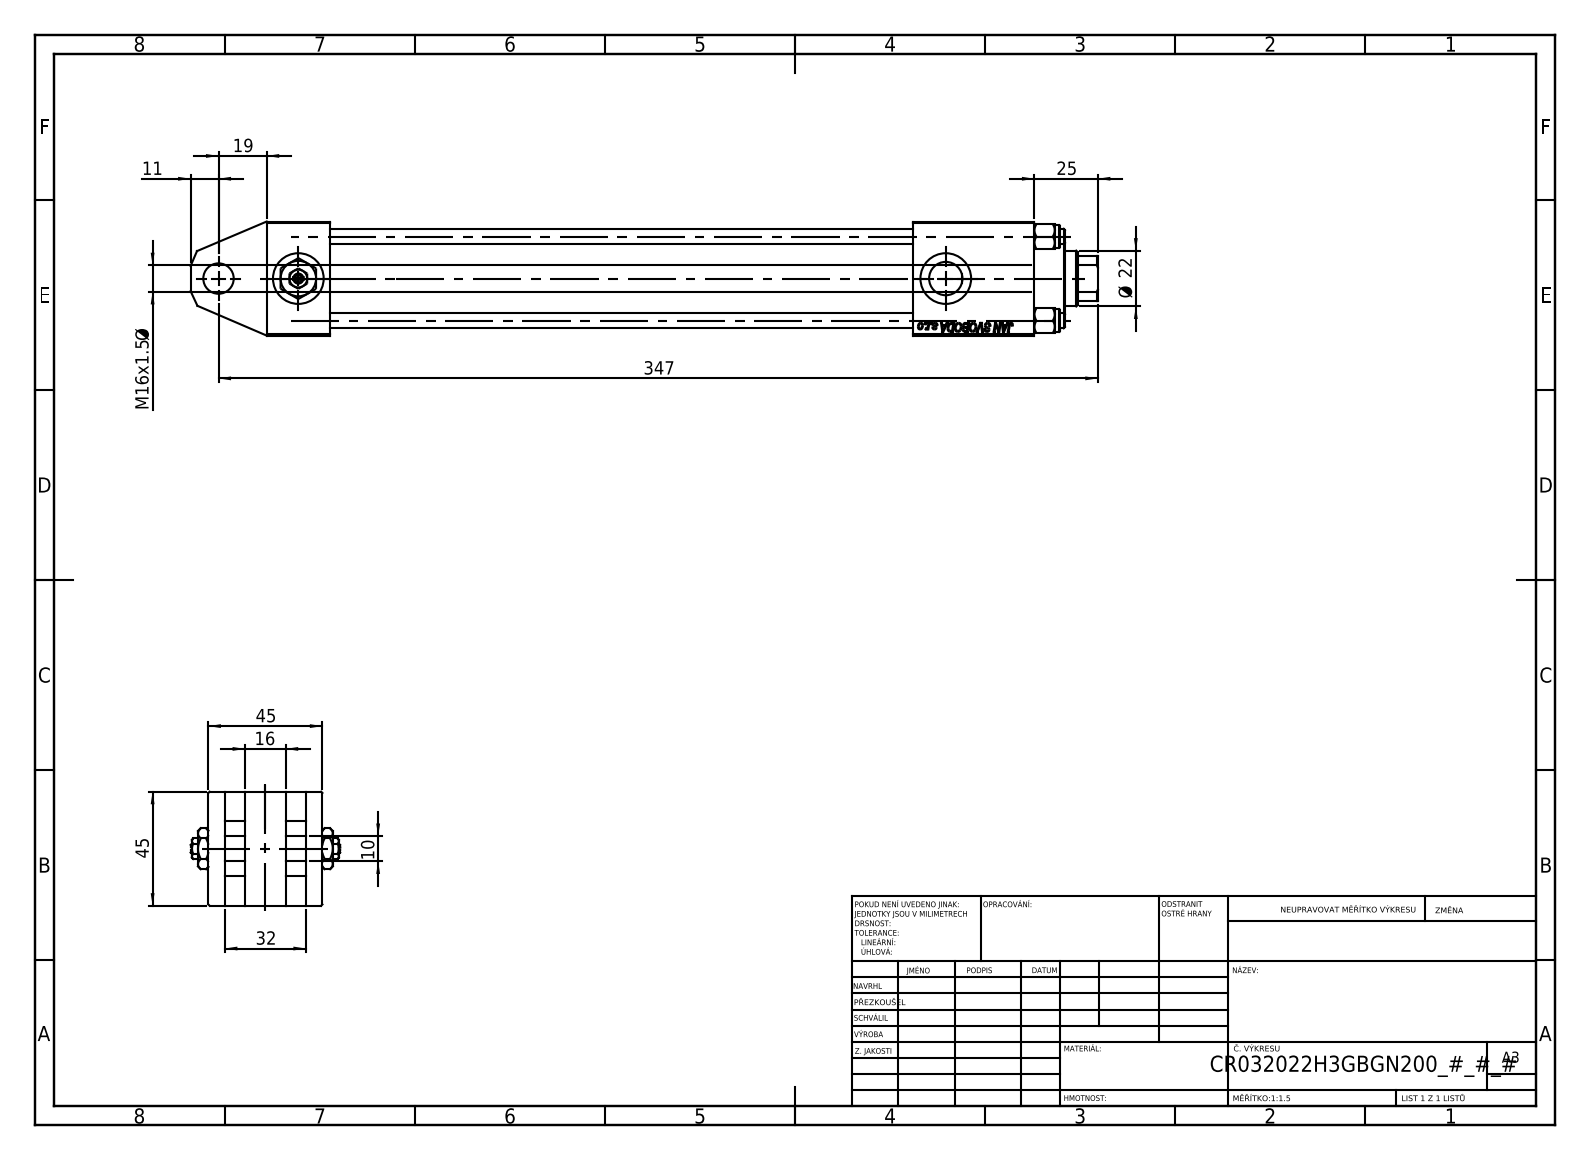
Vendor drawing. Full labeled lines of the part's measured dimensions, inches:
Part name (STEP PRODUCT): Zatka_pro_OIL_PORT; V215CR_VCP_H; V215CR_TYCINKA_H; V215_VC_A (+2 more)
STEP written by: SolidWorks 2019 (CONFIG_CONTROL_DESIGN)
Units: inches
Bodies: 13 solids, 1228 faces (564 planar, 94 cylindrical, 570 other)
Overall size (bounding box): 14.094 × 2.323 × 1.772
Volume: 22.67 in³ · Surface area: 226.1 in²
Round holes (diameter × count): ⌀0.236 ×4, ⌀0.276 ×2, ⌀0.518 ×2, ⌀0.787 ×2, ⌀0.413 ×1, ⌀0.472 ×1, ⌀0.866 ×1, ⌀0.945 ×1, ⌀0.984 ×1, ⌀1.26 ×1, ⌀1.299 ×1
Round bosses / shafts (diameter × count): ⌀0.354 ×4, ⌀1.496 ×1, ⌀1.339 ×1
Partial cylindrical surfaces — rounded edges, fillets, slot ends (radius × count): R0.413 ×1
Main face-to-face distances: 1.772, 0.315, 0.256, 1.516, 0.571, 1.201, 0.945, 0.984, 11.929, 10.039
Hole centre spacings: 0.924, 1.307, 1.848, 1.24, 10.059, 11.299
